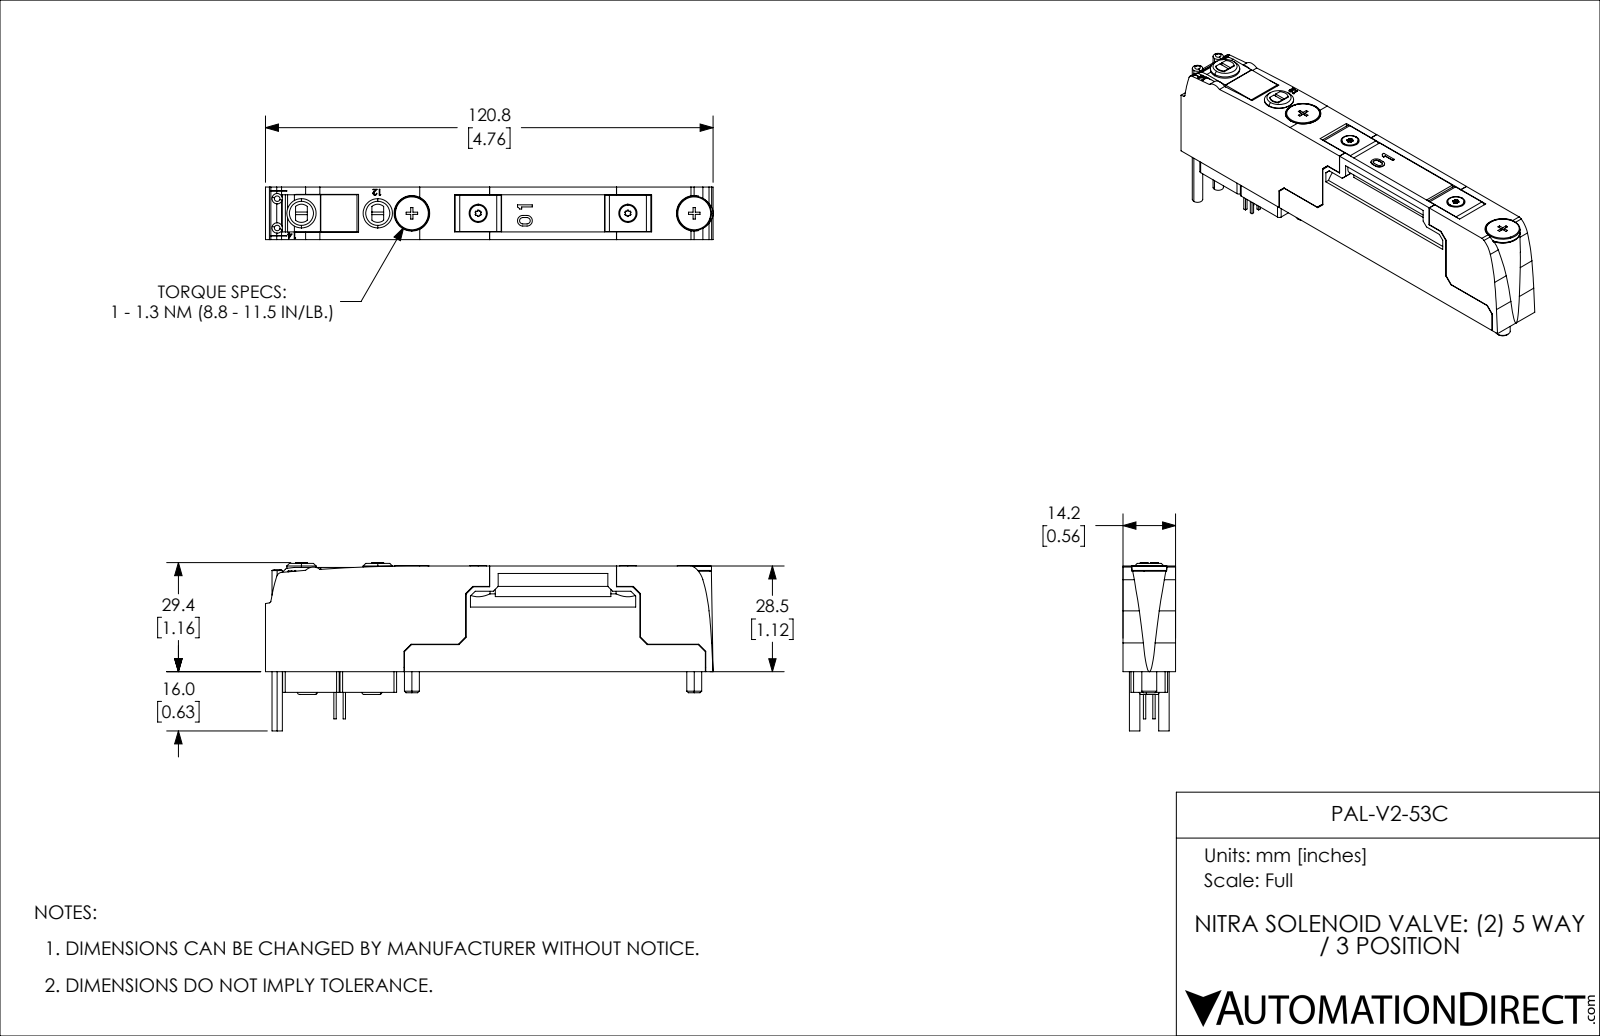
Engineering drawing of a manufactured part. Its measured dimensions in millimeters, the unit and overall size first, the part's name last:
Units: millimetres
Overall size (bounding box): 120.8 × 45.4 × 14.2
Round holes (diameter × count): ⌀3.1 ×2, ⌀4.2 ×2, ⌀9.6 ×1
Round bosses / shafts (diameter × count): ⌀9.3 ×2, ⌀7.9 ×2, ⌀4.4 ×2, ⌀4 ×2, ⌀2.8 ×2
Partial cylindrical surfaces — rounded edges, fillets, slot ends (radius × count): R0.7 ×8, R0.72 ×4, R1.2 ×4, R1.5 ×3, R0.65 ×2, R0.86 ×2, R0.88 ×2, R1.43 ×2
Main face-to-face distances: 14.2, 2.1, 12.1, 2.2, 6.4, 28.5, 17.2, 10, 5.6, 21.2
Hole centre spacings: 10.8, 17.4, 28.2, 76.2, 87, 104.4
Volume: 44 729 mm³ · Surface area: 18 021 mm²
Bodies: 1 solid, 558 faces (396 planar, 125 cylindrical, 37 other)
Part name (STEP PRODUCT): PAL-V2-53C
STEP written by: SolidWorks 2019 (CONFIG_CONTROL_DESIGN)
